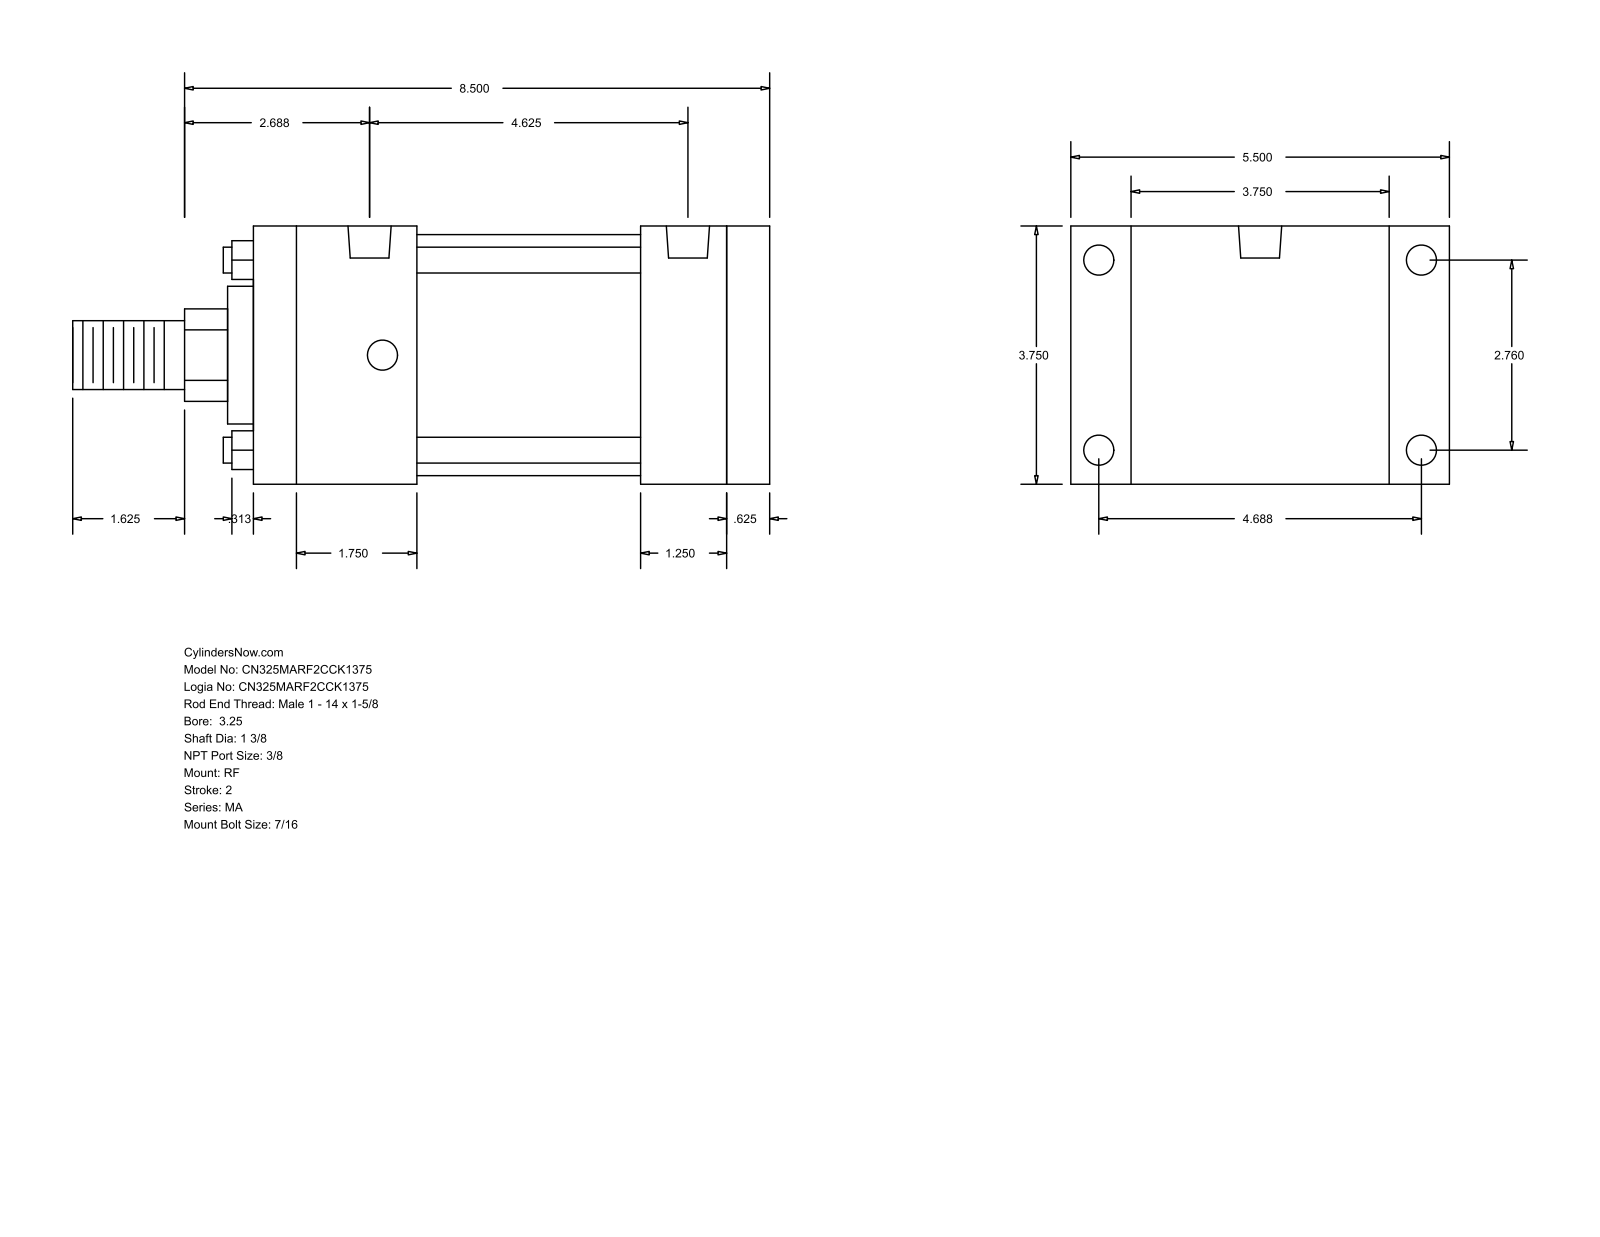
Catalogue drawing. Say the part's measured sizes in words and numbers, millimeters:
The part is named "MA_RF__0325_1.375". Its 3-D file was written by "GSSL Pune (CONFIG_CONTROL_DESIGN)". It is 0 solids with 92 faces: 64 planar, 28 cylindrical and 0 other. Overall it measures 257.18 by 139.7 by 95.25 millimeters. Round holes: 8 of diameter 11.11, 2 of diameter 15.93. Round bosses or shafts: 4 of diameter 9.53, 1 of diameter 88.9, 1 of diameter 50.8, 1 of diameter 34.92, 1 of diameter 25.4. Partial cylindrical surfaces (rounded edges, fillets, slot ends): 1 of radius 17.06. The main face-to-face distances are 95.24, 190.5, 174.63, 15.87, 22.23, 117.47, 142.88, 31.75, 47.62, 60.32. The hole center spacings are 4.77, 70.1, 107.94, 112.71, 119.06, 138.16, 117.48.
